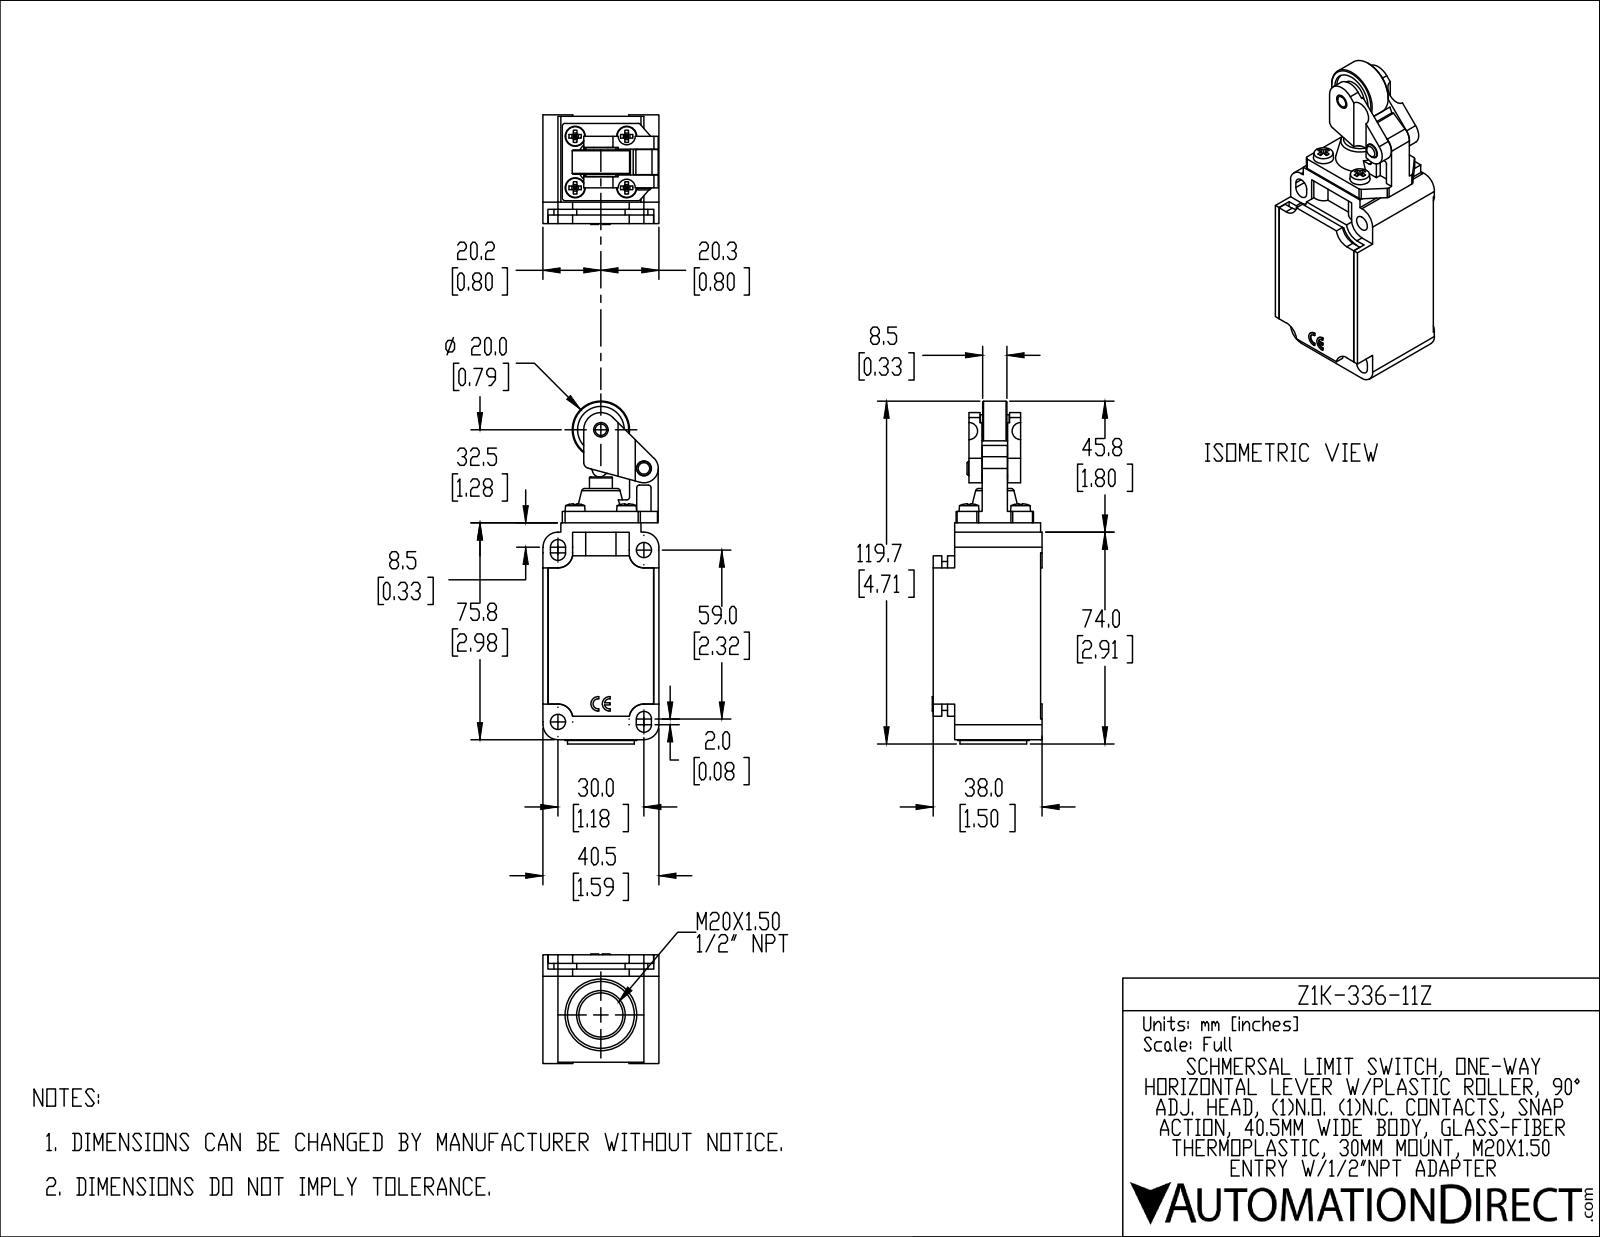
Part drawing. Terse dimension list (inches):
name: Z1K-336-11Z; 101102908_1; 101102908_1_2
written by: SolidWorks 2019 (AUTOMOTIVE_DESIGN)
unit: in
bodies: 2 solids, 319 faces (222 planar, 79 cylindrical, 18 other)
size: 4.713 × 1.594 × 1.508
volume: 6.946 in³; area: 38.55 in²
holes: 2× ⌀0.209, 1× ⌀0.197, 1× ⌀0.205, 1× ⌀0.319, 1× ⌀0.642, 1× ⌀0.669
bosses: 1× ⌀0.984, 1× ⌀0.917, 1× ⌀0.787, 1× ⌀0.413, 1× ⌀0.315, 1× ⌀0.197
rounds: 11× R0.039, 8× R0.205, 8× R0.207, 4× R0.104, 4× R0.283, 3× R0.098, 2× R0.069, 2× R0.118
face distances: 1.594, 1.476, 0.295, 0.177, 1.181, 0.197, 1.201, 1.004, 0.079, 0.118
hole spacings: 0.02, 0.794, 1.122, 1.756, 2.641, 3.679, 4.059
